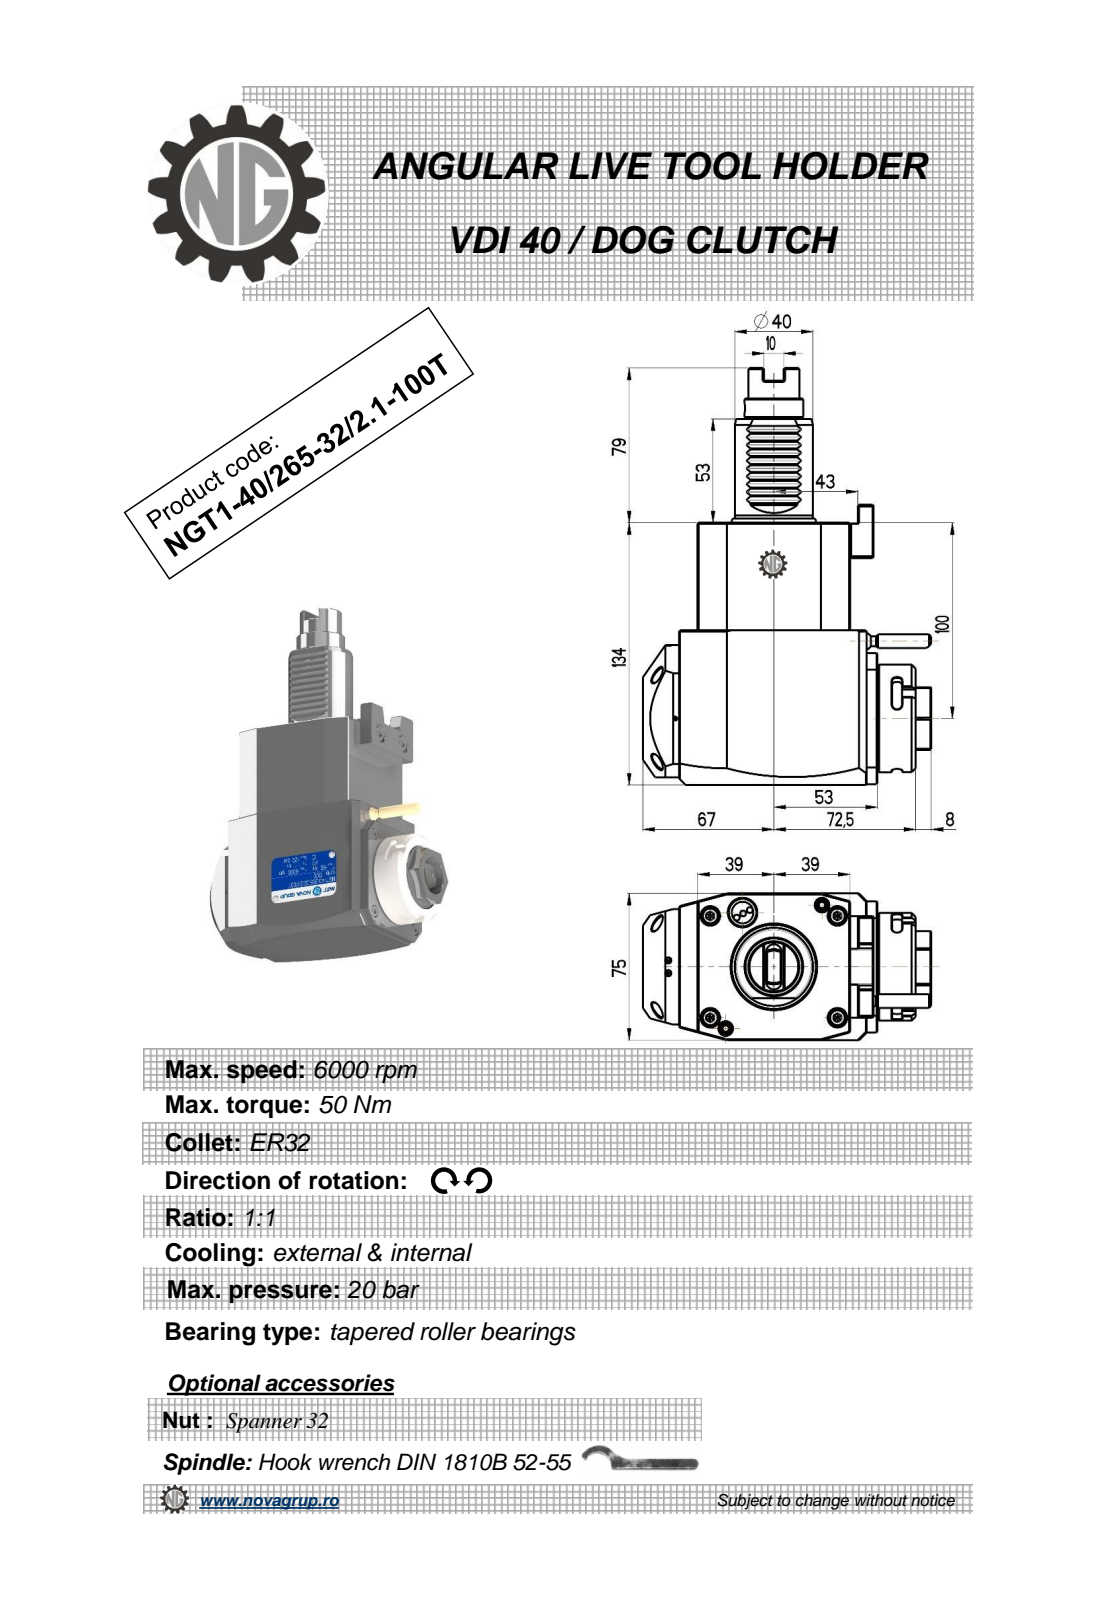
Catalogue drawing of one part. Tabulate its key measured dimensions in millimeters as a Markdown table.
| quantity | value |
| --- | --- |
| part name | NGT1_40_265_32_1_1_100T |
| STEP written by | PRO/ENGINEER BY PARAMETRIC TECHNOLOGY CORPORATION, 2010280 (CONFIG_CONTROL_DESIGN) |
| units | millimeters |
| bodies | 1 solid, 335 faces (210 planar, 63 cylindrical, 62 other) |
| overall size | 213 × 147.5 × 75 |
| volume | 1 083 000 mm³ |
| surface area | 77 922 mm² |
| round holes (diameter × count) | 2.5 × 1, 3 × 1, 4.2 × 1, 23 × 1 |
| round bosses / shafts (diameter × count) | 55 × 1, 48 × 1, 40 × 1, 30 × 1, 26 × 1, 8 × 1, 7 × 1, 5 × 1 |
| partial cylindrical surfaces (radius × count) | 0.3 × 10, 0.26 × 6, 2.5 × 6, 0.5 × 3, 1 × 2, 180 × 2, 12.5 × 1, 24.5 × 1 |
| main face-to-face distances | 75, 134, 78, 14, 92, 19.5, 84.88, 111.5, 33.5, 4 |
| hole center spacings | 43.2, 120.28, 158.5 |
